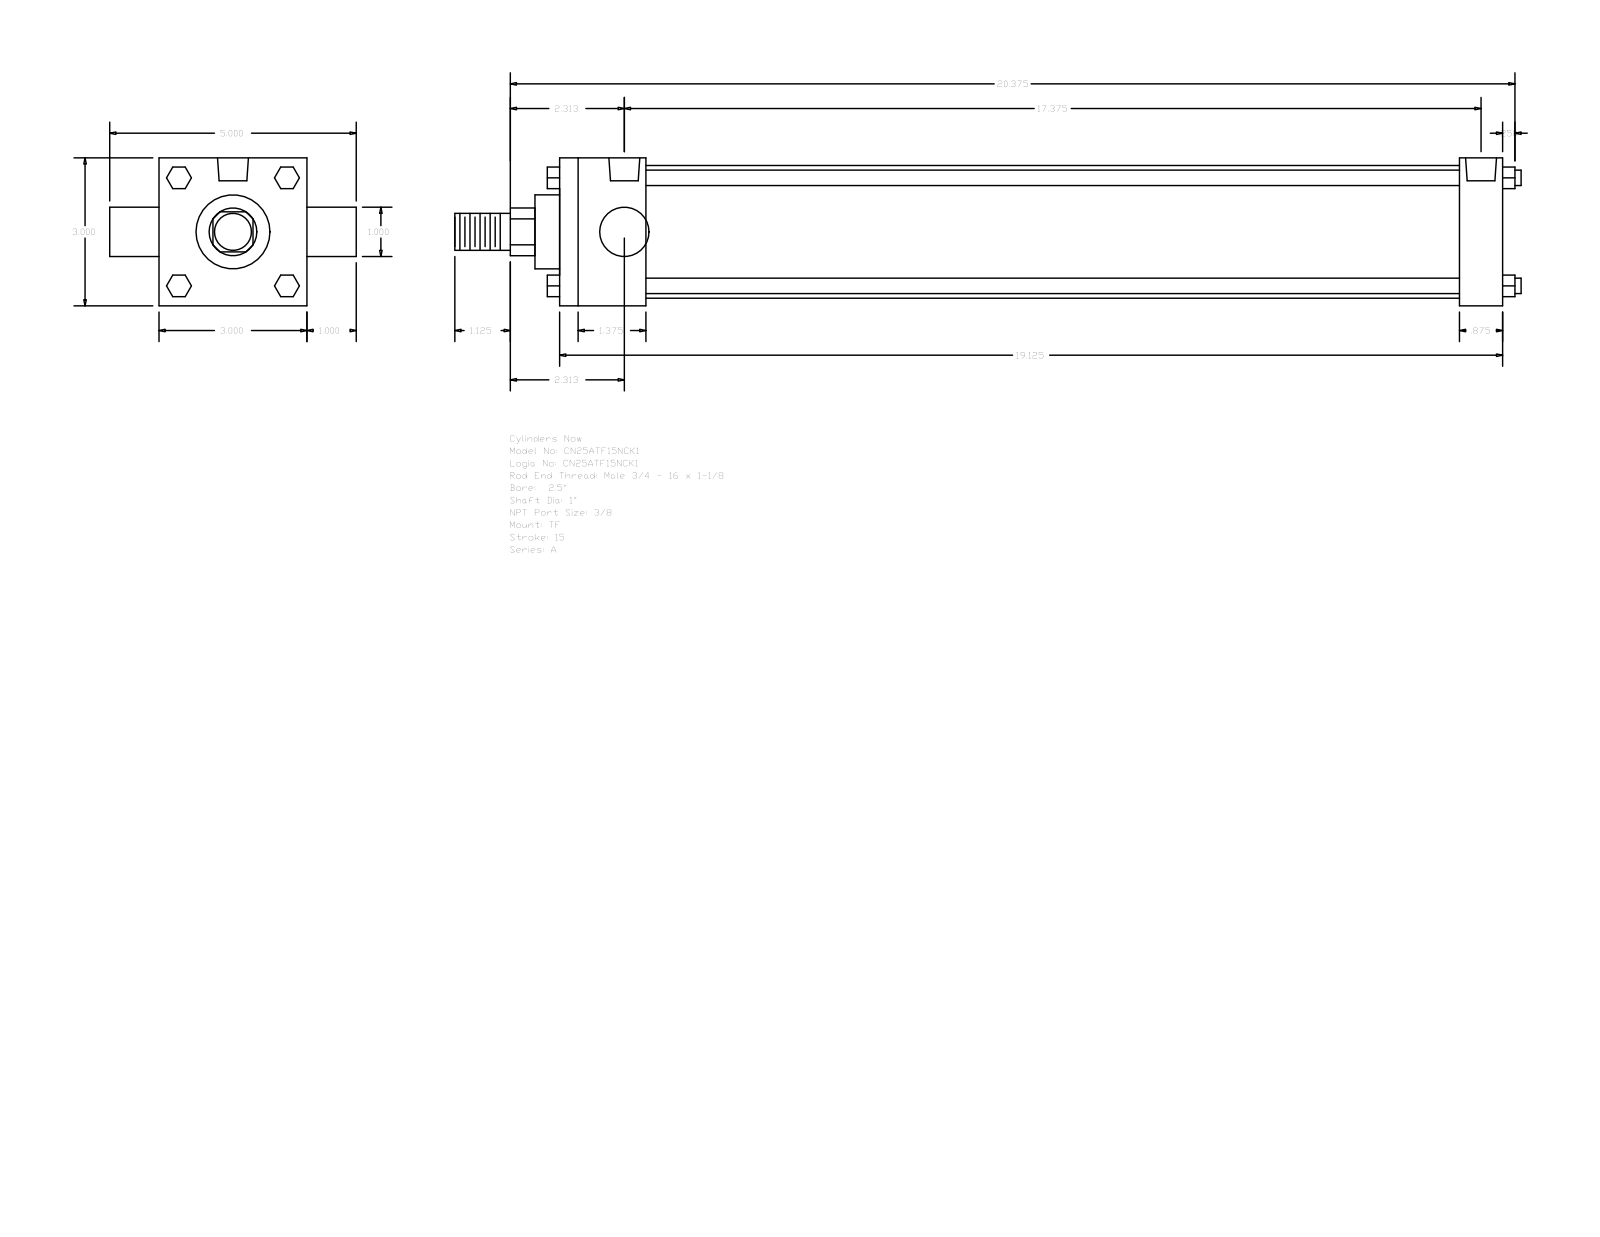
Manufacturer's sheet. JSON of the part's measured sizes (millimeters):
{"part_name": "A_TF__0250_1", "step_written_by": "GSSL Pune (CONFIG_CONTROL_DESIGN)", "units": "millimeters", "bodies": {"solids": 0, "faces": 120, "planar": 92, "cylindrical": 28, "other": 0}, "overall_size": [549.27, 127, 76.2], "round_holes": [[5.56, 3], [15.93, 2]], "round_bosses_or_shafts": [[7.94, 4], [25.4, 2], [68.33, 1], [38.1, 1], [19.05, 1]], "partial_cylinders_radius": [[12.29, 1]], "face_to_face_distances": [76.2, 485.78, 44.45, 463.55, 419.1, 441.33, 22.23, 25.4, 101.6, 12.7], "hole_center_spacings": [2.38, 443.7, 441.32, 446.08]}
